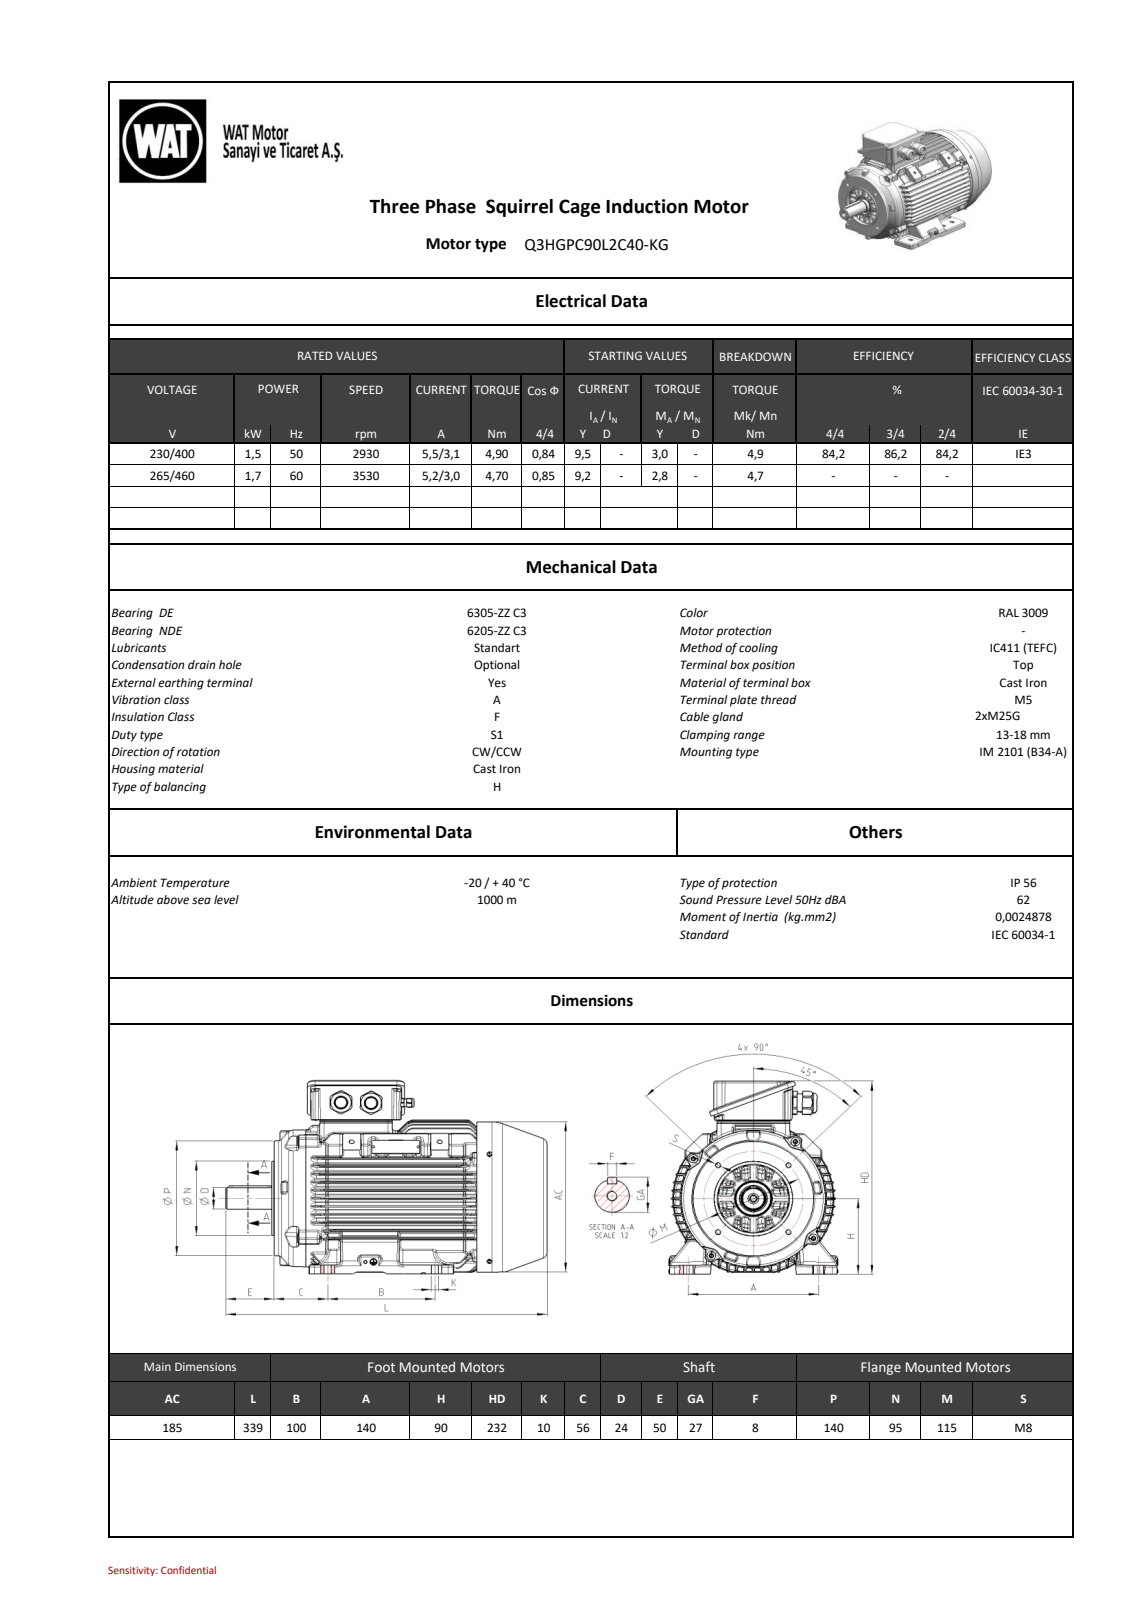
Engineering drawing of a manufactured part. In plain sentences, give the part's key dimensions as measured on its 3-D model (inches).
The part is named "26000A30F4D8rorv". Its 3-D file was written by "SIEMENS PLM Software NX 11.0 (AUTOMOTIVE_DESIGN)". It is 0 solids with 2929 faces: 839 planar, 840 cylindrical and 1250 other. Overall it measures 13.324 by 9.133 by 8.919 inches. Round holes: 5 of diameter 0.268, 3 of diameter 0.165, 3 of diameter 0.394, 2 of diameter 0.098, 2 of diameter 0.677, 1 of diameter 0.256, 1 of diameter 0.331, 1 of diameter 1.453, 1 of diameter 1.461, 1 of diameter 6.85. Round bosses or shafts: 4 of diameter 0.787, 3 of diameter 0.341, 3 of diameter 0.335, 3 of diameter 0.315, 3 of diameter 0.197, 2 of diameter 1.091, 2 of diameter 0.994, 2 of diameter 0.362. Partial cylindrical surfaces (rounded edges, fillets, slot ends): 250 of radius 0.059, 42 of radius 0.039, 38 of radius 0.157, 37 of radius 0.079, 24 of radius 0.197, 20 of radius 0.071, 16 of radius 0.118, 12 of radius 0.008. The main face-to-face distances are 0.474, 9.395, 1.96, 11.355, 2.464, 0.119, 0.118, 0.059, 0.06, 6.4. The hole center spacings are 3.201, 2.263, 4.527, 1.575, 2.264, 2.784, 2.953, 3.749.
